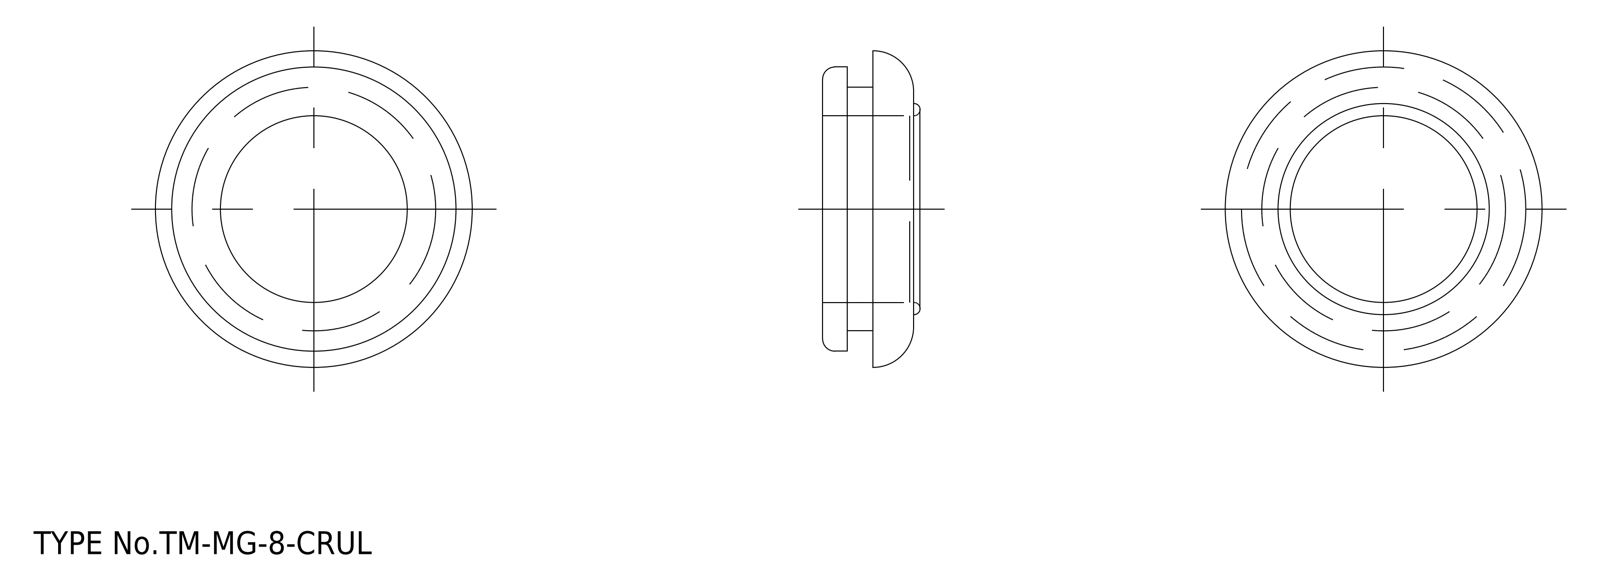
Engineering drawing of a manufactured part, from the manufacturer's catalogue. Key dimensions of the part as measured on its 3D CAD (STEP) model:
Part name (STEP PRODUCT): grommet
STEP written by: spGate 15.6.1 (AUTOMOTIVE_DESIGN)
Units: millimetres
Bodies: 1 solid, 22 faces (6 planar, 10 cylindrical, 6 other)
Overall size (bounding box): 39 × 39 × 12
Volume: 6 082 mm³ · Surface area: 4 647 mm²
Round holes (diameter × count): ⌀23 ×1
Round bosses / shafts (diameter × count): ⌀35 ×1, ⌀30 ×1, ⌀26 ×1
Main face-to-face distances: 5, 0.5, 4.5, 11.2, 10.7, 6.2, 8.2, 7.7, 3.2, 3
